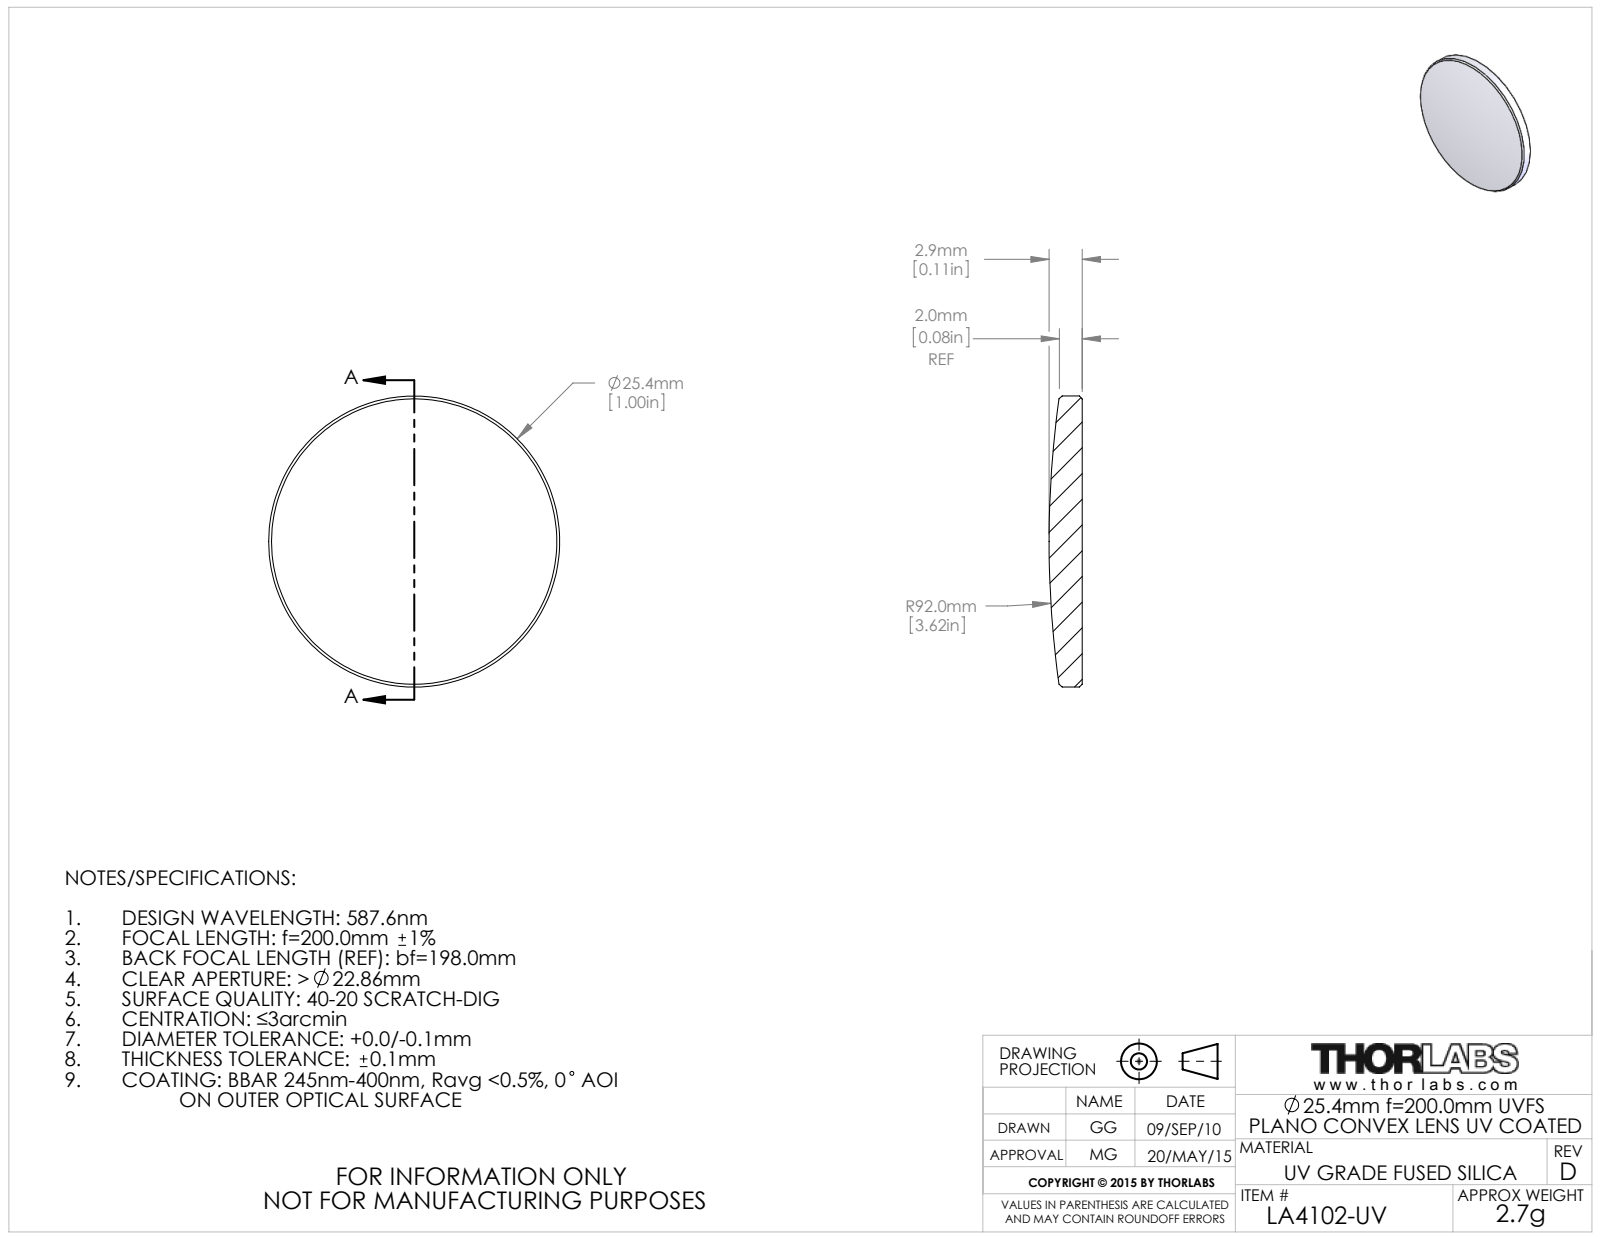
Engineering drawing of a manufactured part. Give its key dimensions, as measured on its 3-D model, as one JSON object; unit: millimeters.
{"part_name": "4286-E0W", "step_written_by": "SolidWorks 2014 (CONFIG_CONTROL_DESIGN)", "units": "millimeters", "bodies": {"solids": 1, "faces": 9, "planar": 1, "cylindrical": 2, "other": 6}, "overall_size": [25.4, 25.4, 2.9], "volume_mm3": 1235, "surface_area_mm2": 1154, "round_bosses_or_shafts": [[25.4, 1]]}
